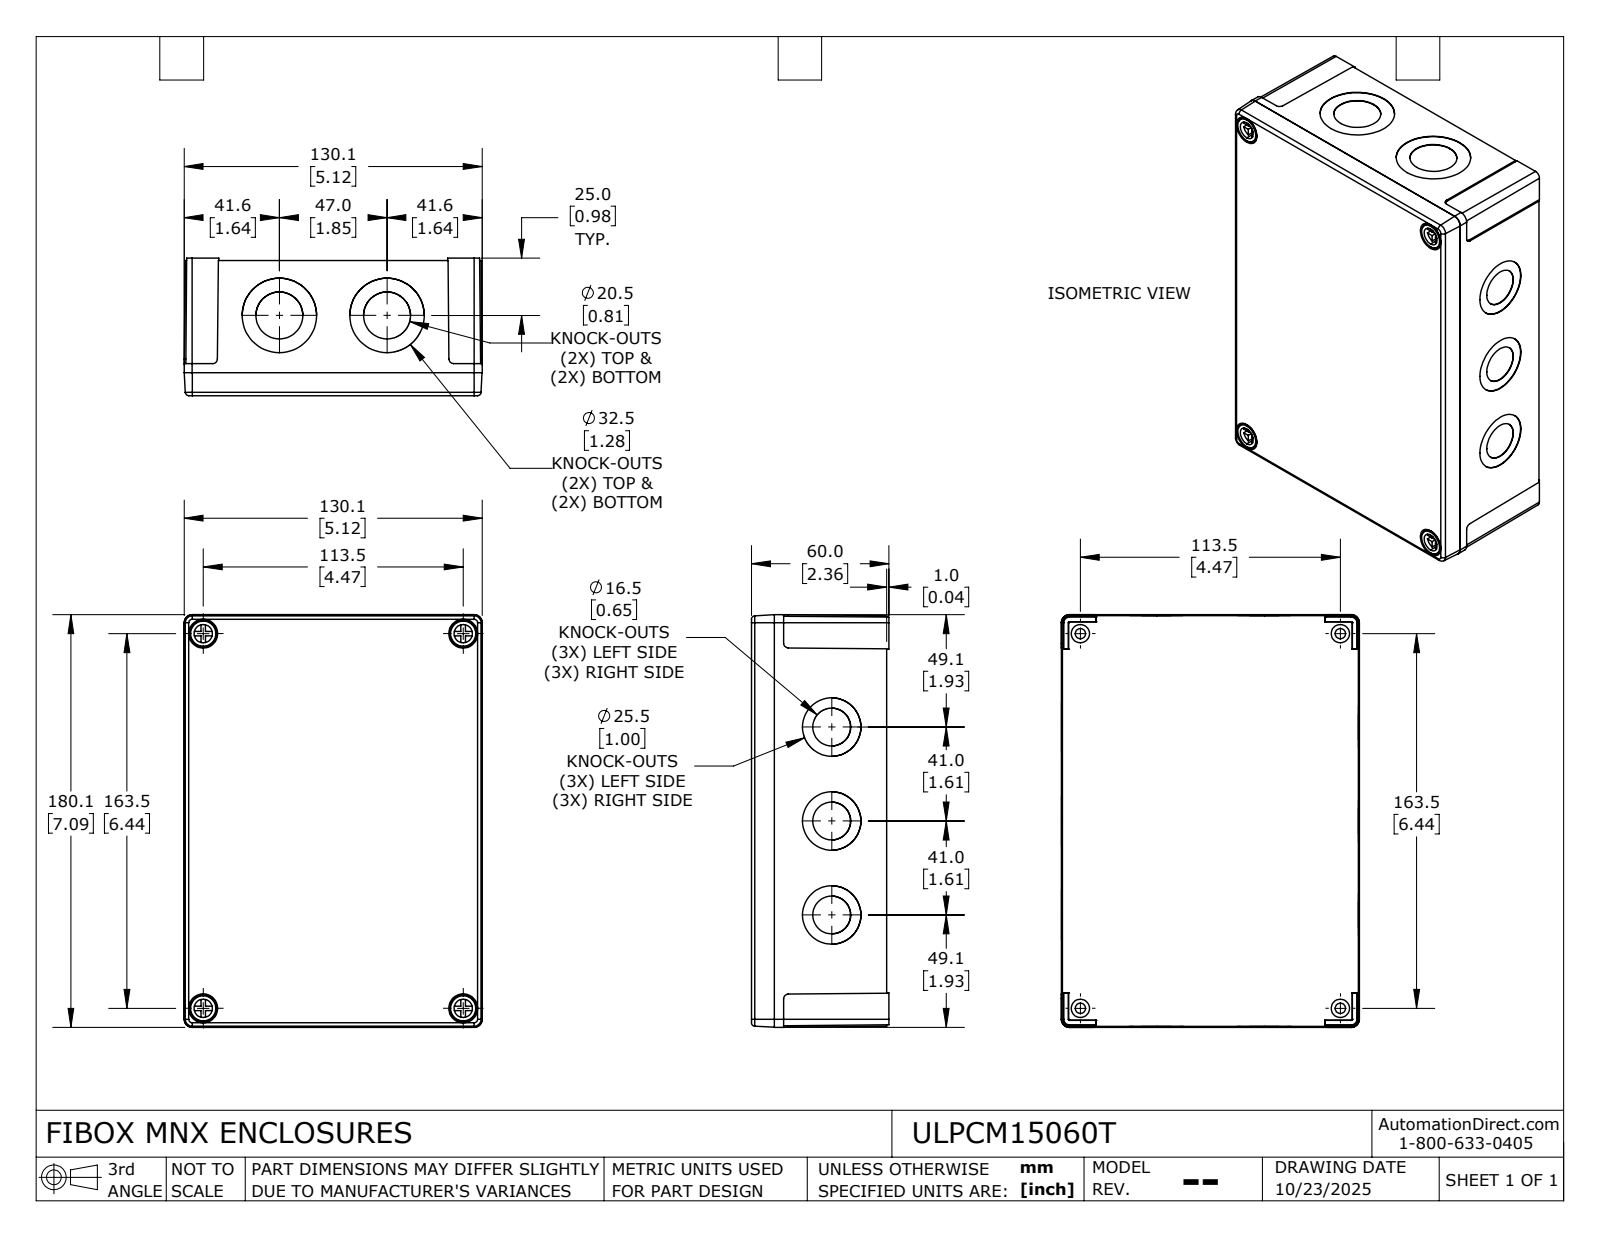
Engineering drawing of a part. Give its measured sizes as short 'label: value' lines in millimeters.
name: ULPCM15060T_Default
written by: SolidWorks 2024 (CONFIG_CONTROL_DESIGN)
unit: mm
bodies: 6 solids, 549 faces (285 planar, 212 cylindrical, 52 other)
size: 180.1 × 130.1 × 60
volume: 295 000 mm³; area: 172 200 mm²
holes: 8× ⌀3.2, 8× ⌀4, 6× ⌀16.5, 6× ⌀25.5, 4× ⌀4.5, 4× ⌀8, 4× ⌀11.6, 4× ⌀20.5, 4× ⌀32.5
bosses: 8× ⌀8, 8× ⌀2.5, 4× ⌀11, 4× ⌀7.2
rounds: 16× R1, 6× R1.4, 4× R0.5, 4× R1.5, 4× R2, 4× R5, 2× R0.6
face distances: 59, 3.2, 55.8, 3, 56, 52.8, 4.2, 49, 10, 46
hole spacings: 33.9, 41, 49.3, 50, 57.9, 82.6, 83.2, 103
